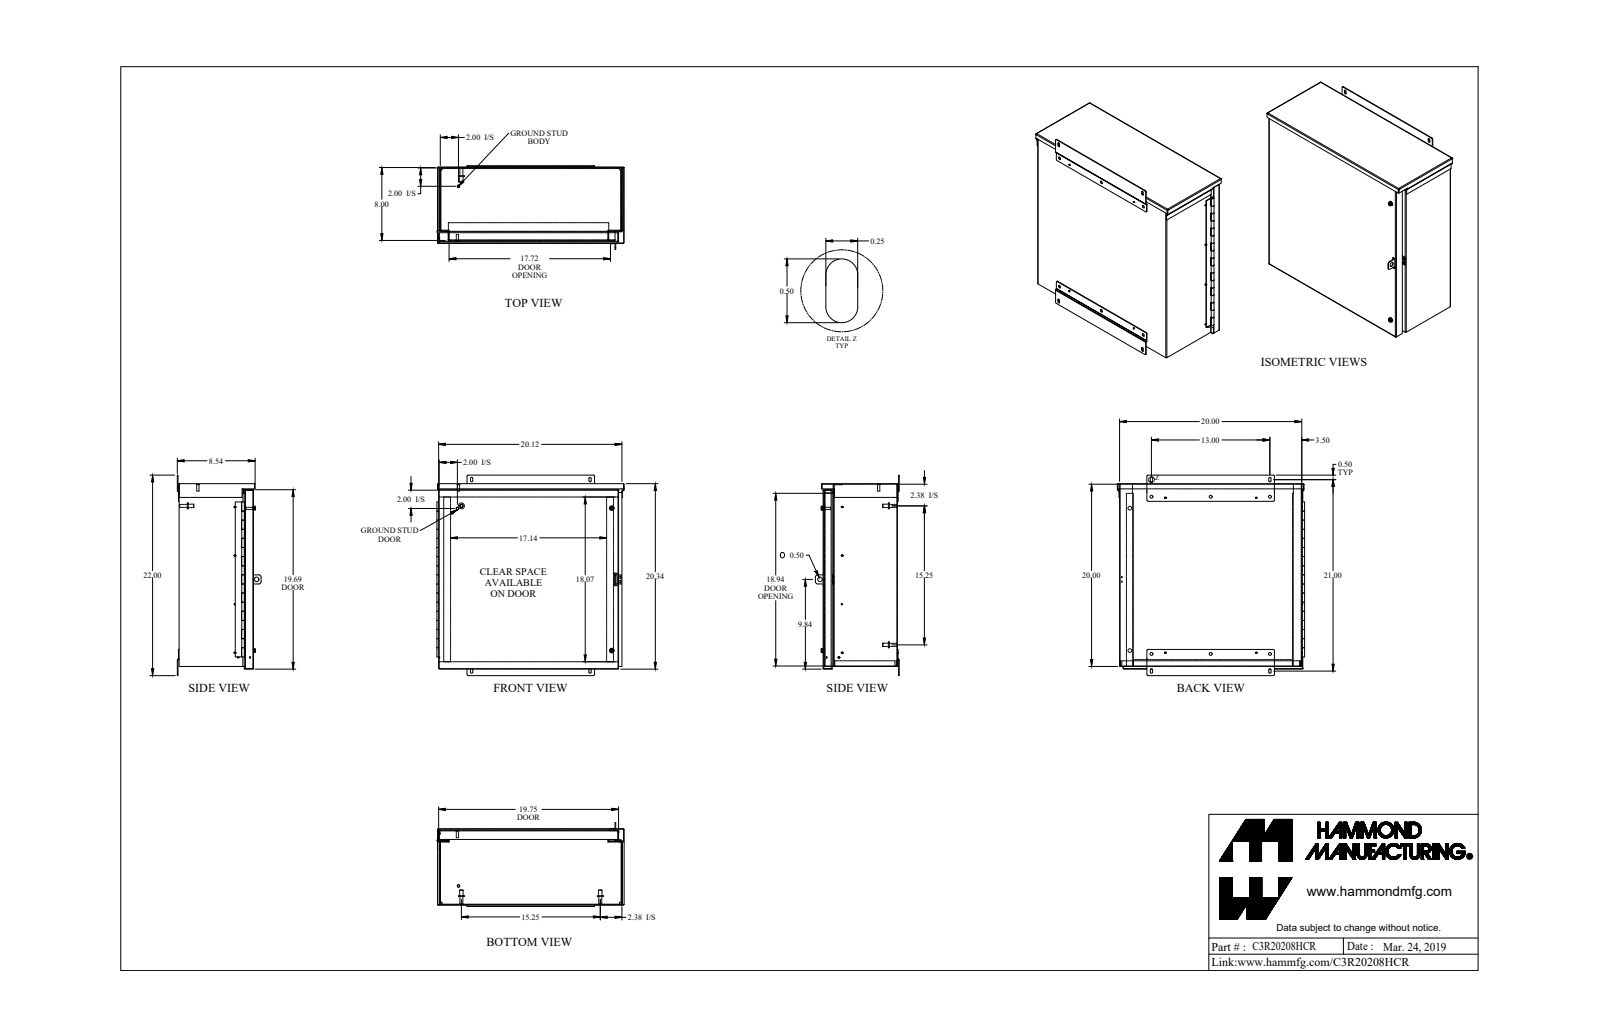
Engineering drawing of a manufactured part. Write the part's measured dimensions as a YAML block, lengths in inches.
part_name: "C3R20208HCR_Default"
step_written_by: "SolidWorks 2019 (CONFIG_CONTROL_DESIGN)"
units: inches
bodies: {solids: 33, faces: 860, planar: 487, cylindrical: 319, other: 54}
overall_size: [22, 20.556, 9.197]
volume: 116.2
surface_area: 3812
round_holes:
  - {diameter: 0.313, count: 9}
  - {diameter: 0.14, count: 4}
  - {diameter: 0.26, count: 3}
  - {diameter: 0.137, count: 2}
  - {diameter: 0.266, count: 2}
  - {diameter: 0.28, count: 2}
  - {diameter: 0.29, count: 2}
  - {diameter: 0.397, count: 2}
  - {diameter: 0.188, count: 1}
  - {diameter: 0.5, count: 1}
round_bosses_or_shafts:
  - {diameter: 0.131, count: 10}
  - {diameter: 0.65, count: 4}
  - {diameter: 0.375, count: 4}
  - {diameter: 0.33, count: 4}
  - {diameter: 0.51, count: 3}
  - {diameter: 0.244, count: 3}
  - {diameter: 0.187, count: 3}
  - {diameter: 0.5, count: 2}
partial_cylinders:
  - {radius: 0.029, count: 26}
  - {radius: 0.086, count: 26}
  - {radius: 0.125, count: 19}
  - {radius: 0.036, count: 5}
  - {radius: 0.108, count: 5}
  - {radius: 0.171, count: 3}
  - {radius: 0.25, count: 2}
face_to_face_distances: [0.057, 8.1, 20, 19.943, 8.043, 8.157, 20.057, 19.886, 0.943, 6.943]
hole_center_spacings: [1.505, 5.002, 6.5, 11.501, 17.84, 2.409, 4.043, 7.615]
